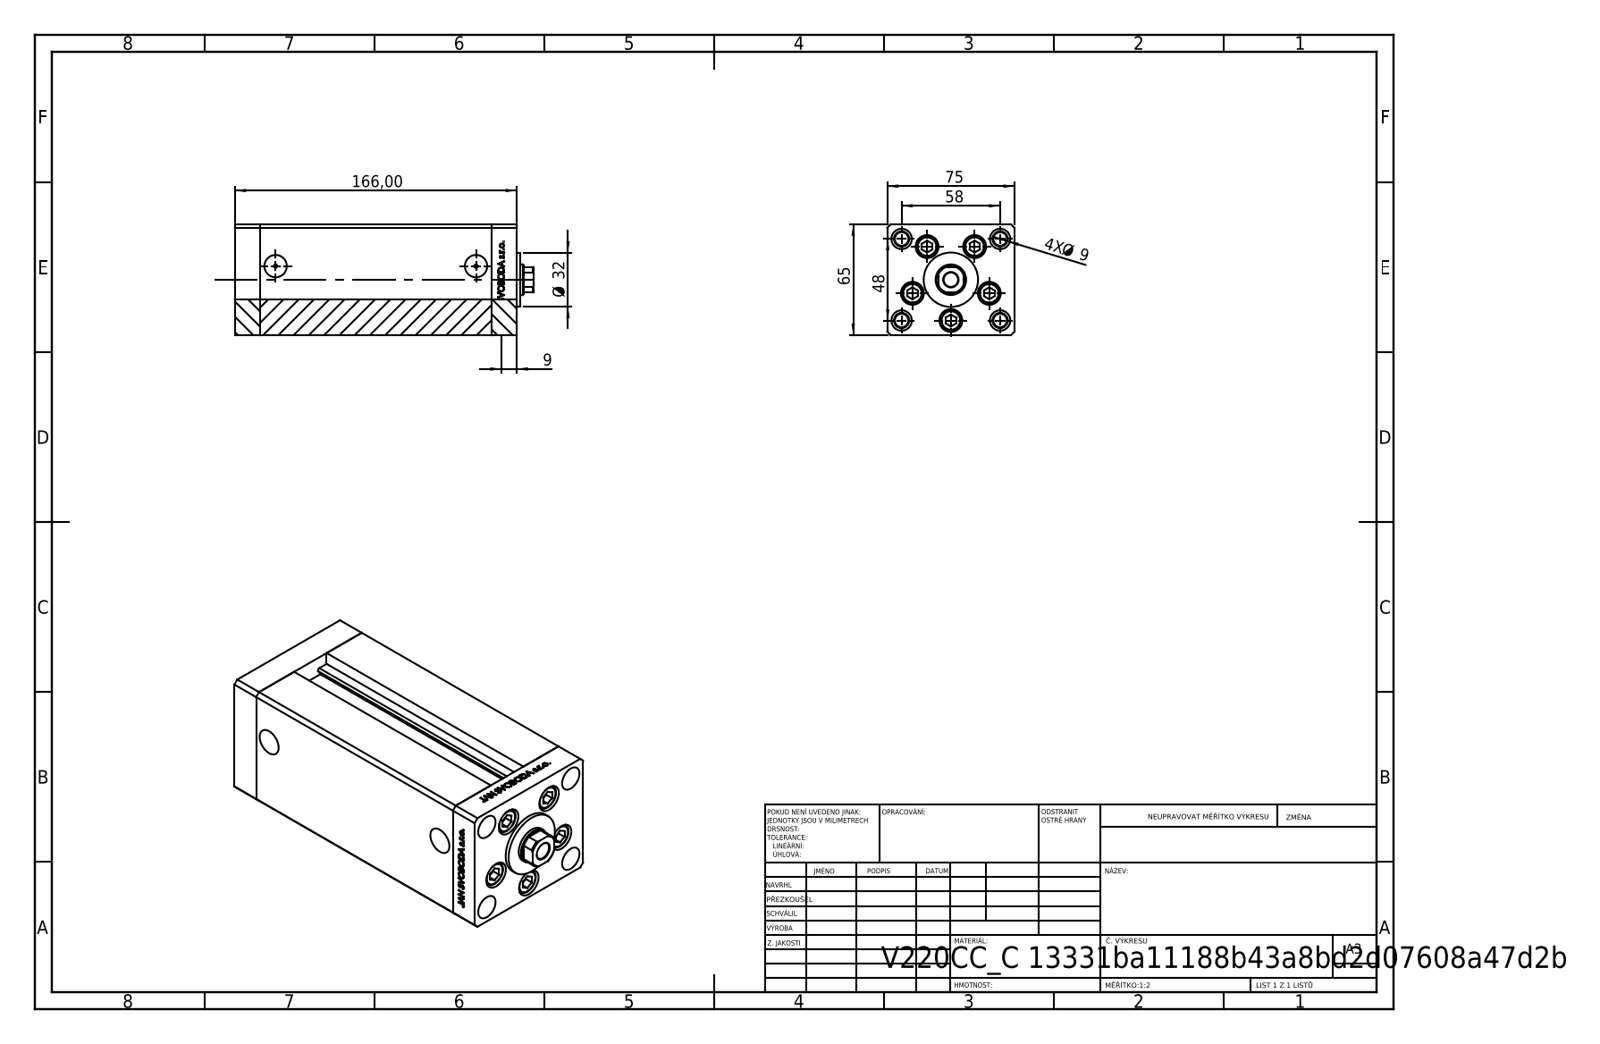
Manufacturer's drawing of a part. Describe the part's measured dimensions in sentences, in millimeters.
The part is named "V220C_C MIDDLE; V220C FRONT; V220C BACK_C; V220C_VC_C (+1 more)". Its 3-D file was written by "SolidWorks 2019 (CONFIG_CONTROL_DESIGN)". It is 13 solids with 1169 faces: 540 planar, 167 cylindrical and 462 other. Overall it measures 176 by 75 by 65 millimeters. Its volume is 680 499 cubic millimeters and its surface area 142 517 square millimeters. Round holes: 9 of diameter 9, 5 of diameter 13.5, 4 of diameter 8, 4 of diameter 12, 2 of diameter 2, 2 of diameter 13.16, 1 of diameter 8.5, 1 of diameter 12.5, 1 of diameter 18. Round bosses or shafts: 5 of diameter 8, 4 of diameter 12.5, 1 of diameter 32. Partial cylindrical surfaces (rounded edges, fillets, slot ends): 2 of radius 0.93, 1 of radius 8.5. The main face-to-face distances are 75, 65, 15, 136, 151, 166, 28, 142, 13, 9. The hole center spacings are 24, 37.64, 15.67, 17.22, 27.71, 28.83, 29, 32.63.
